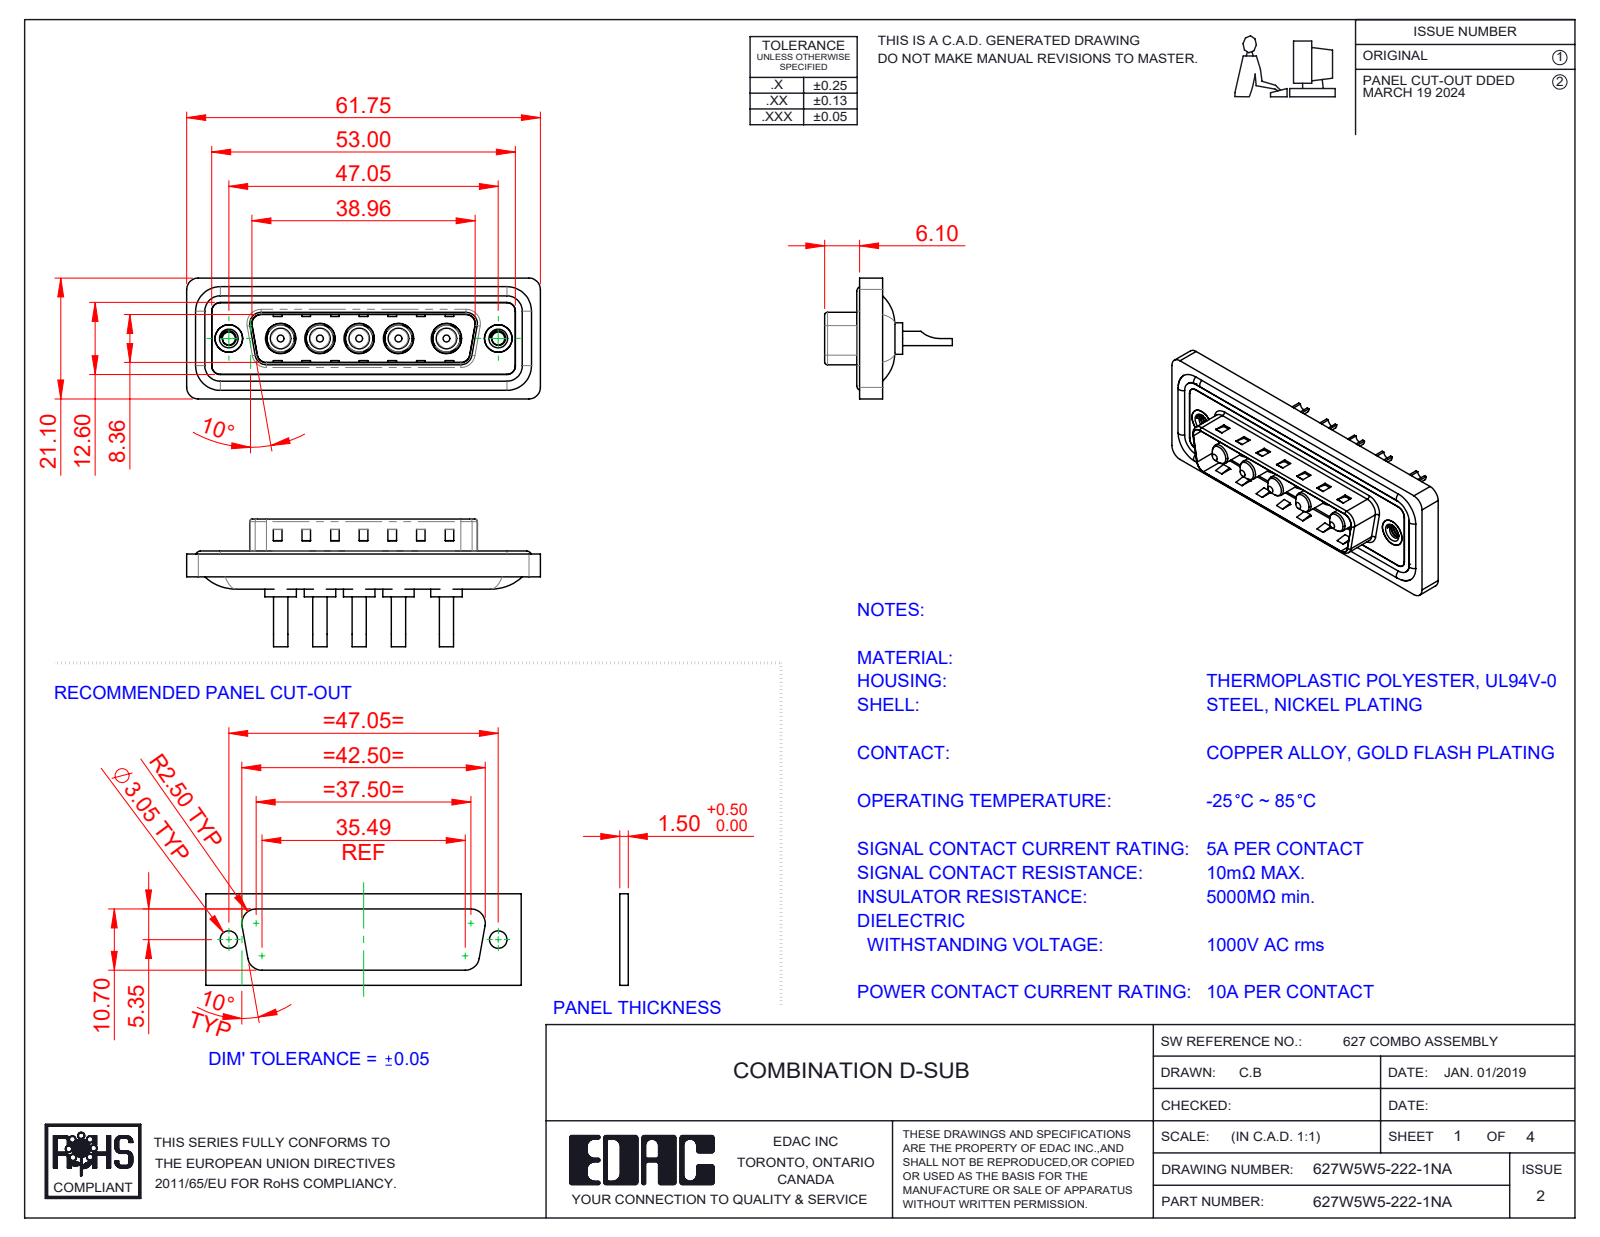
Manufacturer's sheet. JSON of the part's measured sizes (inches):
{"part_name": "627W5W5-222-1NA; 627Combo Waterproof Housing_25 Contacts; Power Pin_10A SC; 627Combo Housing_5W5 (+3 more)", "step_written_by": "SolidWorks 2023 (CONFIG_CONTROL_DESIGN)", "units": "inches", "bodies": {"solids": 17, "faces": 706, "planar": 269, "cylindrical": 300, "other": 137}, "overall_size": [2.431, 0.878, 0.831], "volume_in3": 0.455, "surface_area_in2": 18.65, "round_holes": [[0.067, 5], [0.191, 5], [0.209, 5], [0.089, 2], [0.157, 2], [0.189, 2], [0.197, 2]], "round_bosses_or_shafts": [[0.217, 5], [0.205, 5], [0.187, 5], [0.148, 5], [0.142, 5], [0.098, 5], [0.063, 4], [0.193, 2]], "partial_cylinders_radius": [[0.059, 22], [0.079, 18], [0.02, 8], [0.063, 8], [0.083, 5], [0.01, 4], [0.024, 4], [0.026, 4]], "face_to_face_distances": [0.016, 0.059, 0.02, 0.043, 0.122, 0.063, 0.114, 0.032, 0.377, 0.222], "hole_center_spacings": [0.27, 0.356, 0.541, 1.496, 0.27, 0.33, 0.33, 0.356]}
